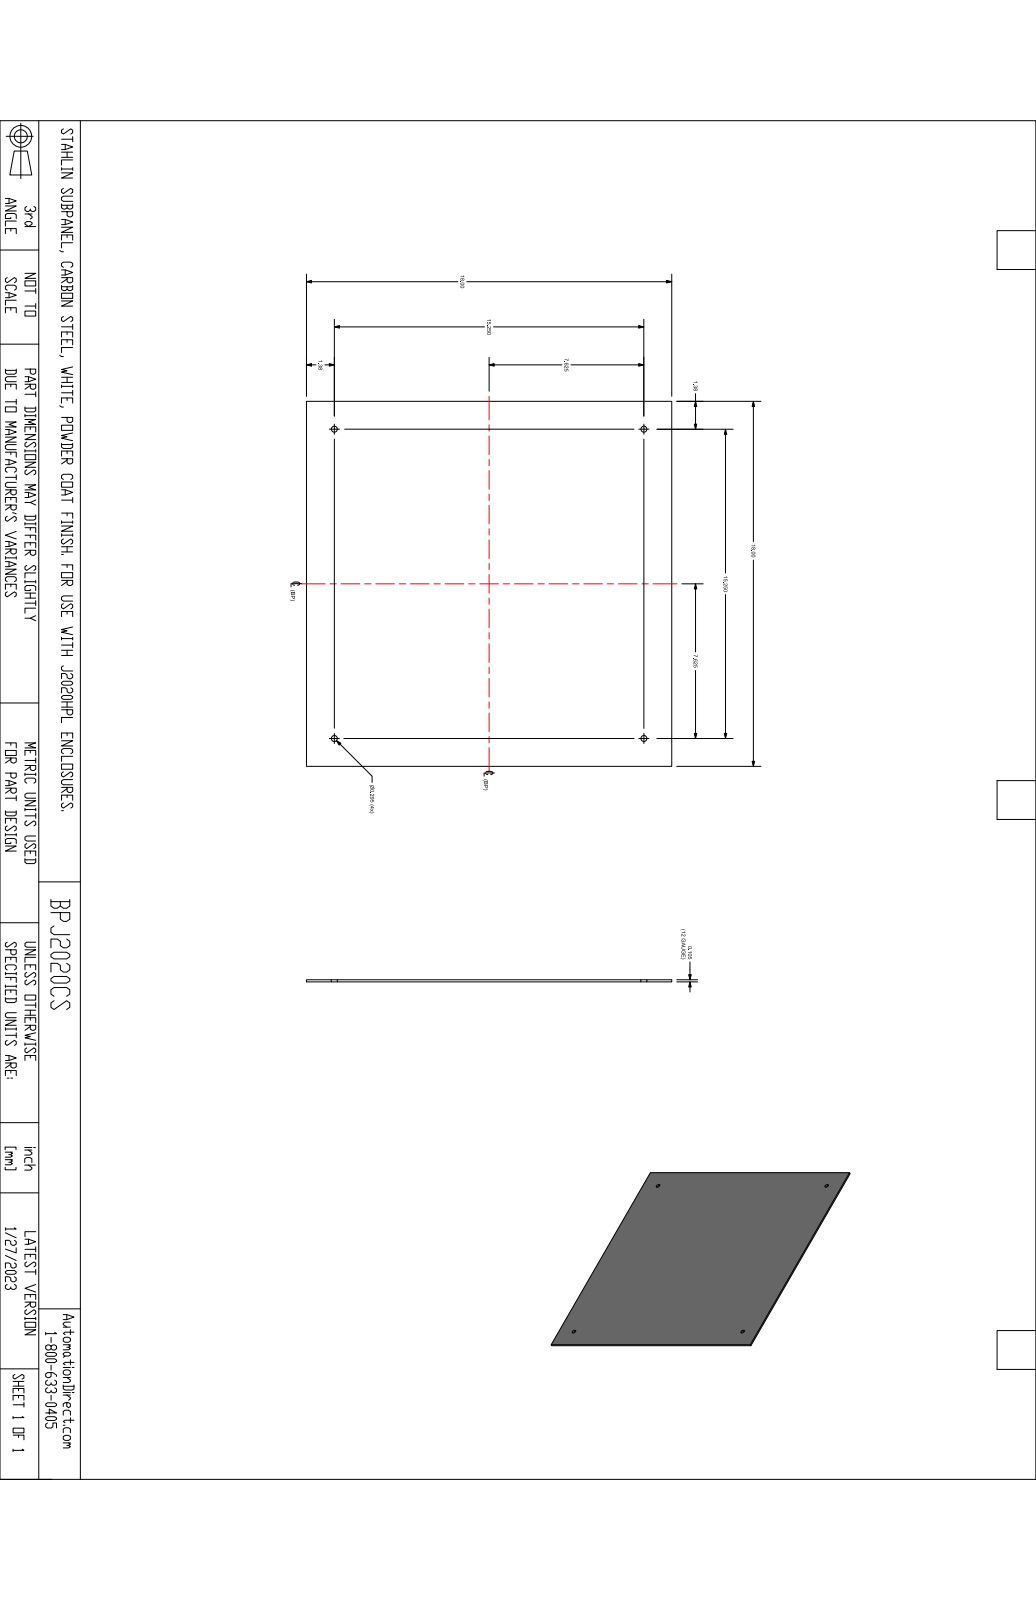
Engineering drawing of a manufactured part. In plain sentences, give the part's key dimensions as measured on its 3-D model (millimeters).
The part is named "HW-MP2020CS". Its 3-D file was written by "Autodesk Inventor 2017 (CONFIG_CONTROL_DESIGN)". It is 1 solid with 10 faces: 6 planar, 4 cylindrical and 0 other. Overall it measures 457.2 by 457.2 by 2.67 millimeters. Its volume is 557 017 cubic millimeters and its surface area 422 839 square millimeters. Round holes: 4 of diameter 7.49. The main face-to-face distances are 2.67, 457.2. The hole center spacings are 387.35, 547.8.
